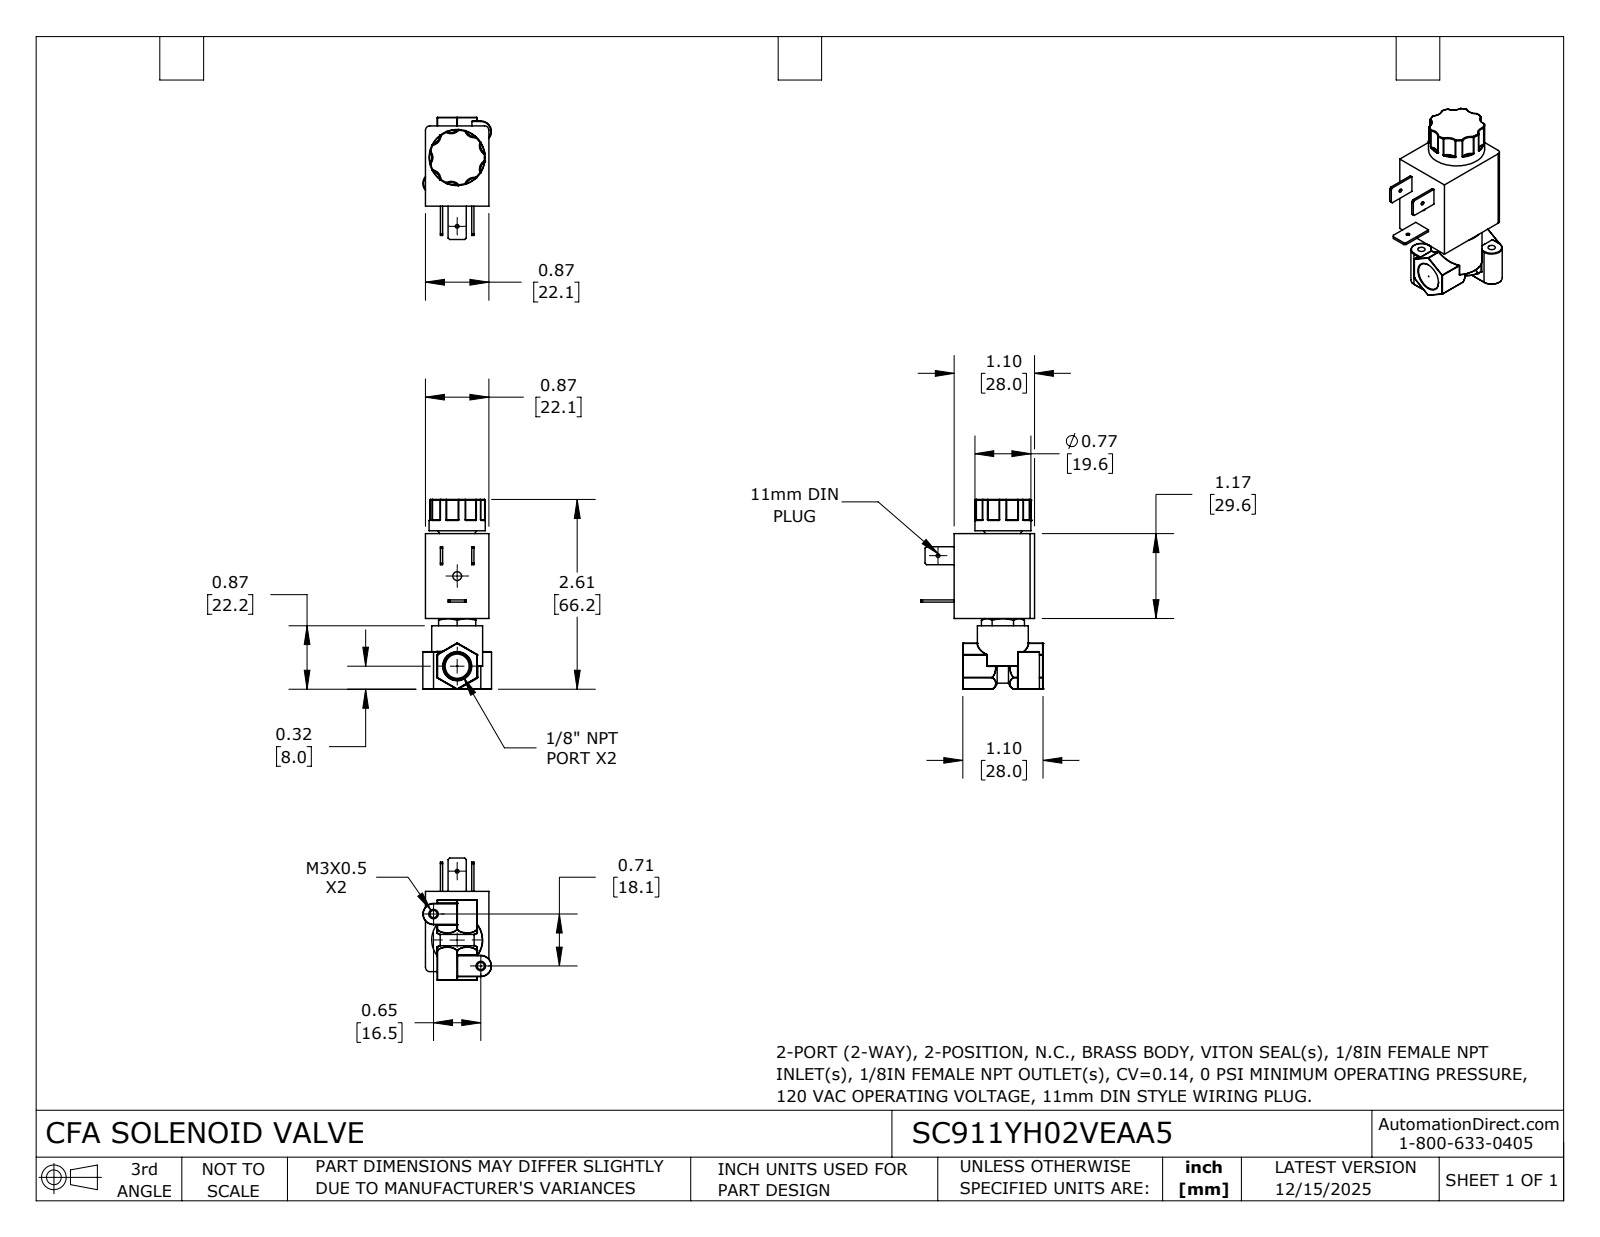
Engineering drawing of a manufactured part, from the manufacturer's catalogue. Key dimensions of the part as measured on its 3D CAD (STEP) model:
Part name (STEP PRODUCT): SC911YH02VEAA5
STEP written by: SolidWorks 2024 (CONFIG_CONTROL_DESIGN)
Units: inches
Bodies: 1 solid, 393 faces (76 planar, 108 cylindrical, 209 other)
Overall size (bounding box): 2.608 × 1.678 × 0.942
Volume: 1.713 in³ · Surface area: 14.37 in²
Round holes (diameter × count): ⌀0.05 ×2, ⌀0.1 ×2, ⌀0.12 ×1
Round bosses / shafts (diameter × count): ⌀0.77 ×1, ⌀0.7 ×1, ⌀0.332 ×1
Partial cylindrical surfaces — rounded edges, fillets, slot ends (radius × count): R0.004 ×27, R0.01 ×18, R0.008 ×12, R0.133 ×7, R0.017 ×2, R0.06 ×2, R0.132 ×2, R0.146 ×2
Main face-to-face distances: 0.87, 1.104, 1.167, 1.637, 0.47, 0.548, 0.161, 0.709, 1.207, 0.04
Hole centre spacings: 0.672, 0.965, 1.342
